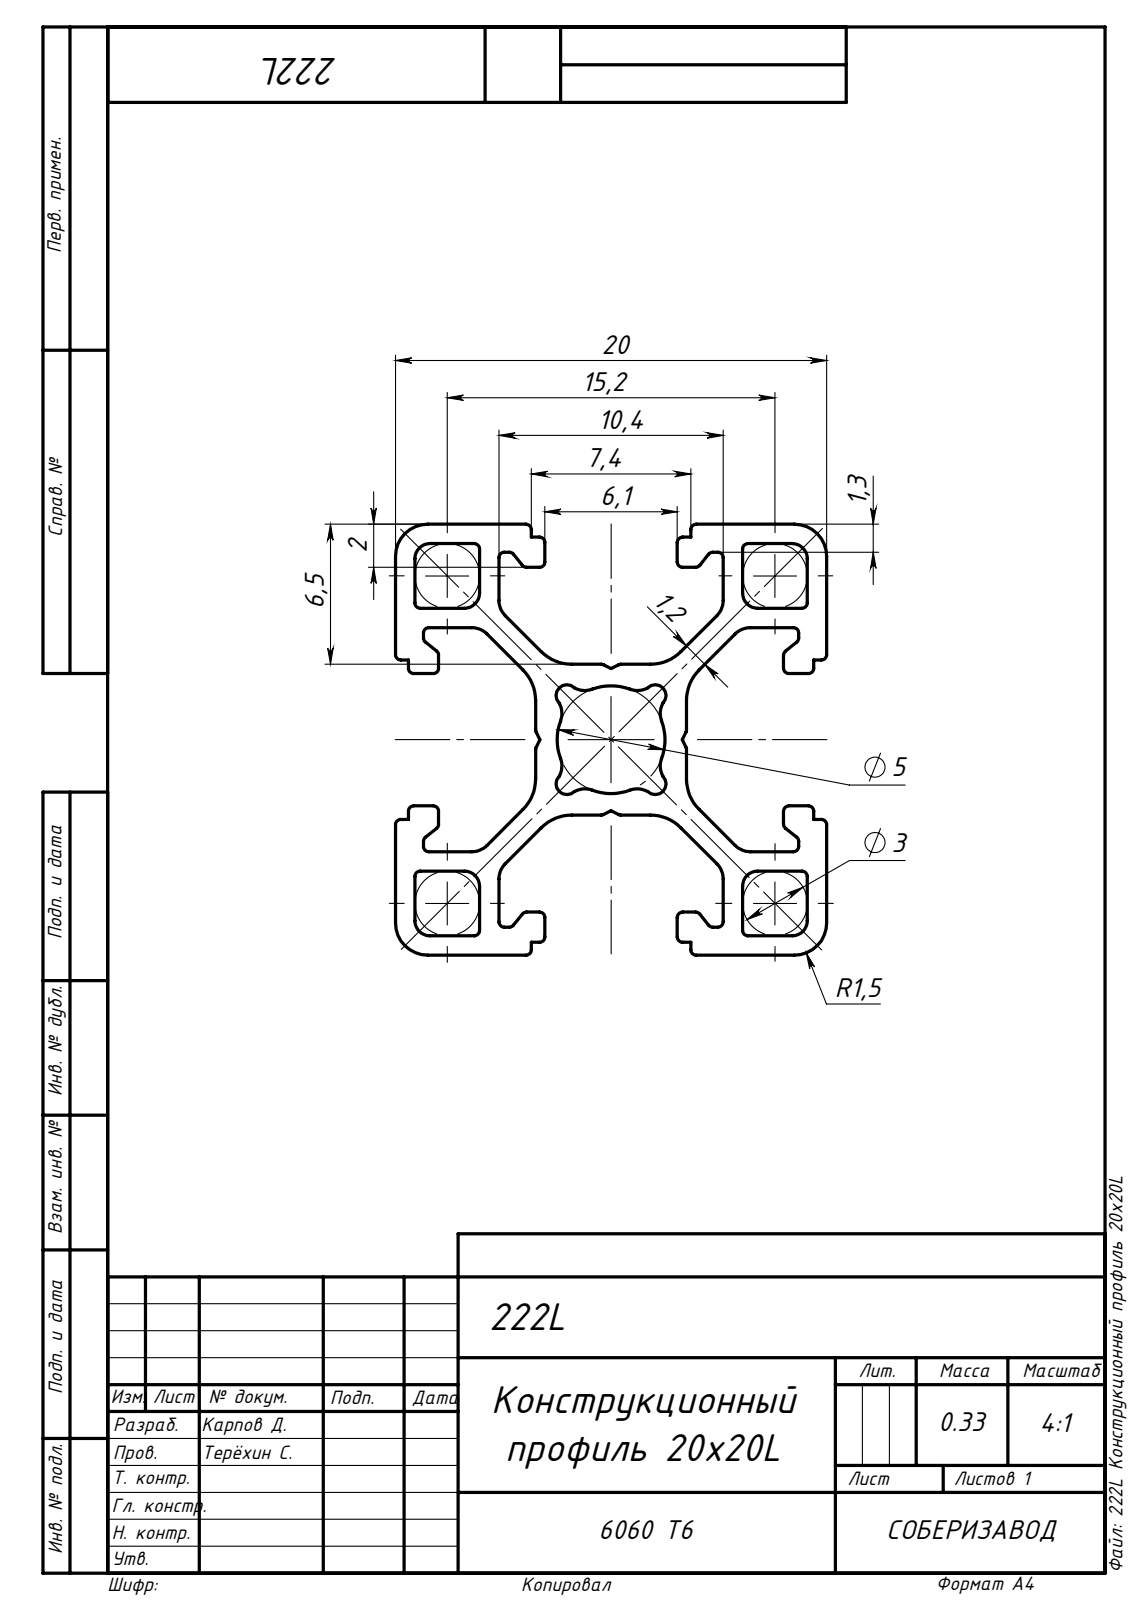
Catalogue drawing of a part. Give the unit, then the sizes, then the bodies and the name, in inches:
Units: inches
Overall size (bounding box): 39.37 × 0.787 × 0.787
Partial cylindrical surfaces — rounded edges, fillets, slot ends (radius × count): R0.01 ×64, R0.039 ×16, R0.028 ×8, R0.079 ×8, R0.02 ×4, R0.059 ×4, R0.098 ×1
Main face-to-face distances: 0.035, 0.154, 0.598, 0.787, 0.752, 0.634, 0.118, 0.189, 0.563, 0.445
Volume: 7.424 in³ · Surface area: 342.1 in²
Bodies: 1 solid, 214 faces (106 planar, 108 cylindrical, 0 other)
STEP written by: SolidWorks 2018 (AUTOMOTIVE_DESIGN)
